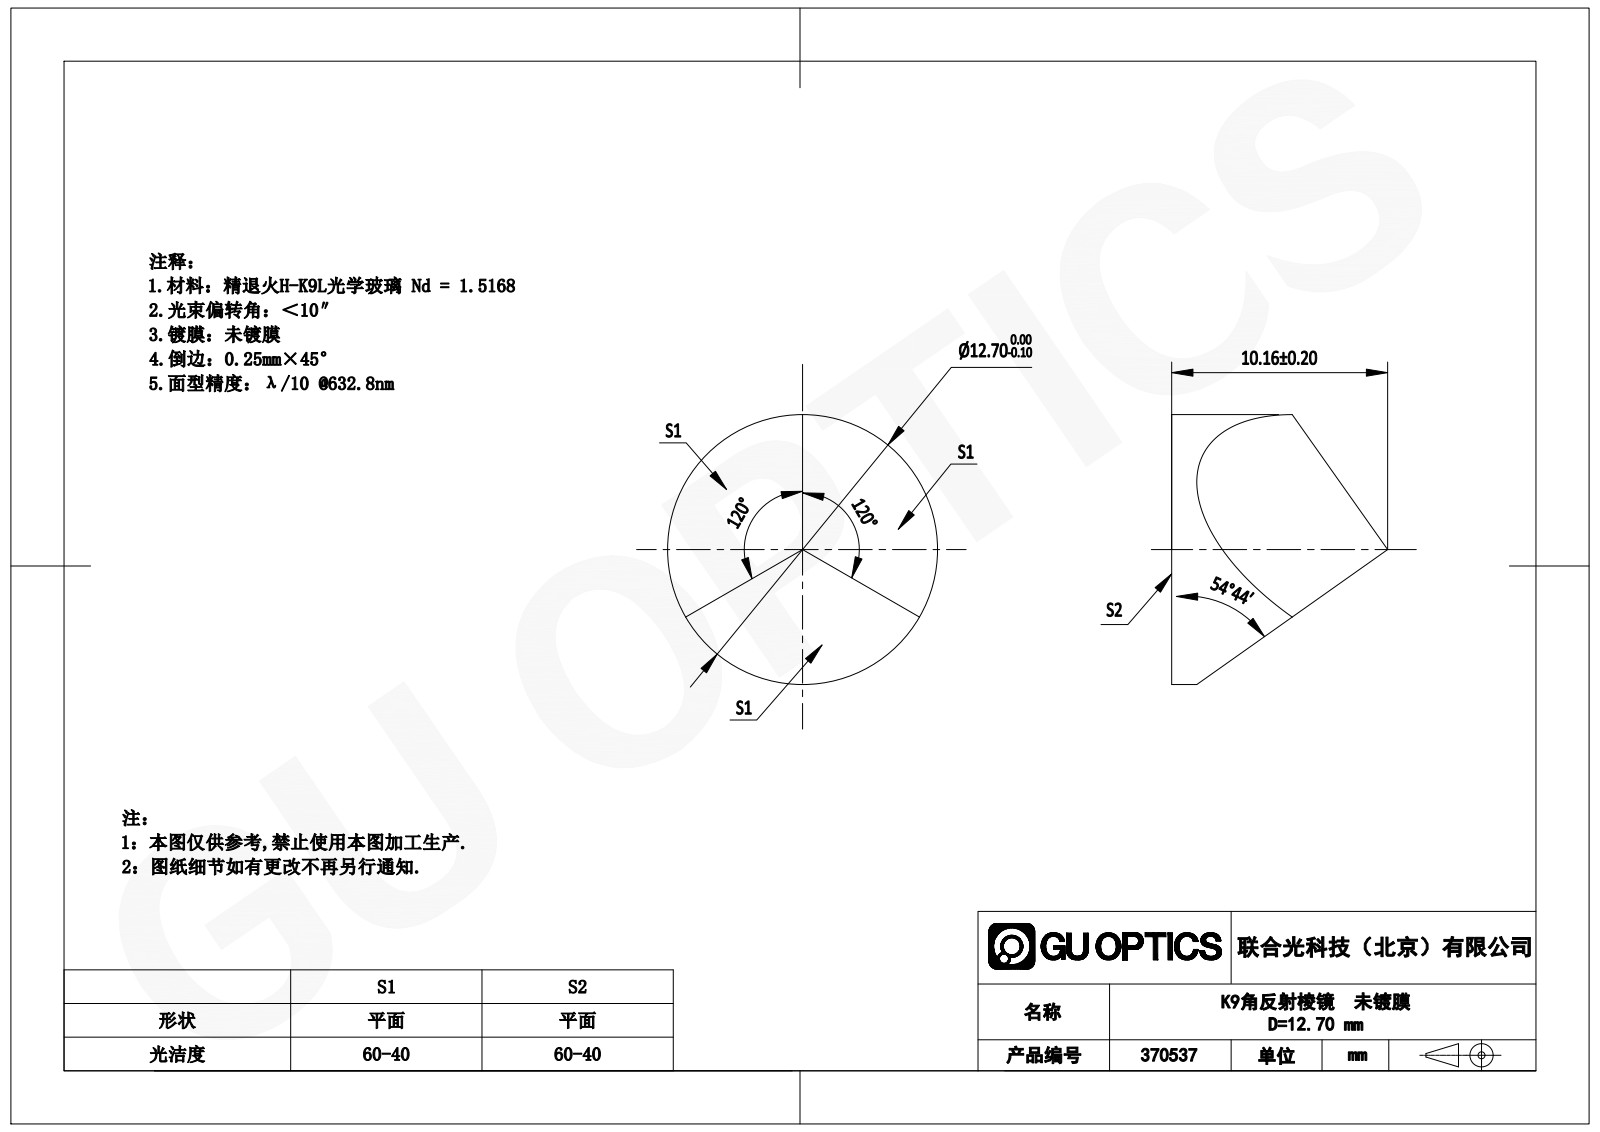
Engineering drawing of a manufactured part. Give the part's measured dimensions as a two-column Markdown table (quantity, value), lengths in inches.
| quantity | value |
| --- | --- |
| part name | GP16-012-2 |
| STEP written by | SolidWorks 2022 (AUTOMOTIVE_DESIGN) |
| units | inches |
| bodies | 1 solid, 12 faces (8 planar, 2 cylindrical, 2 other) |
| overall size | 0.5 × 0.5 × 0.395 |
| volume | 0.04 in³ |
| surface area | 0.699 in² |
| round bosses / shafts (diameter × count) | 0.5 × 1 |
| main face-to-face distances | 0.395 |
